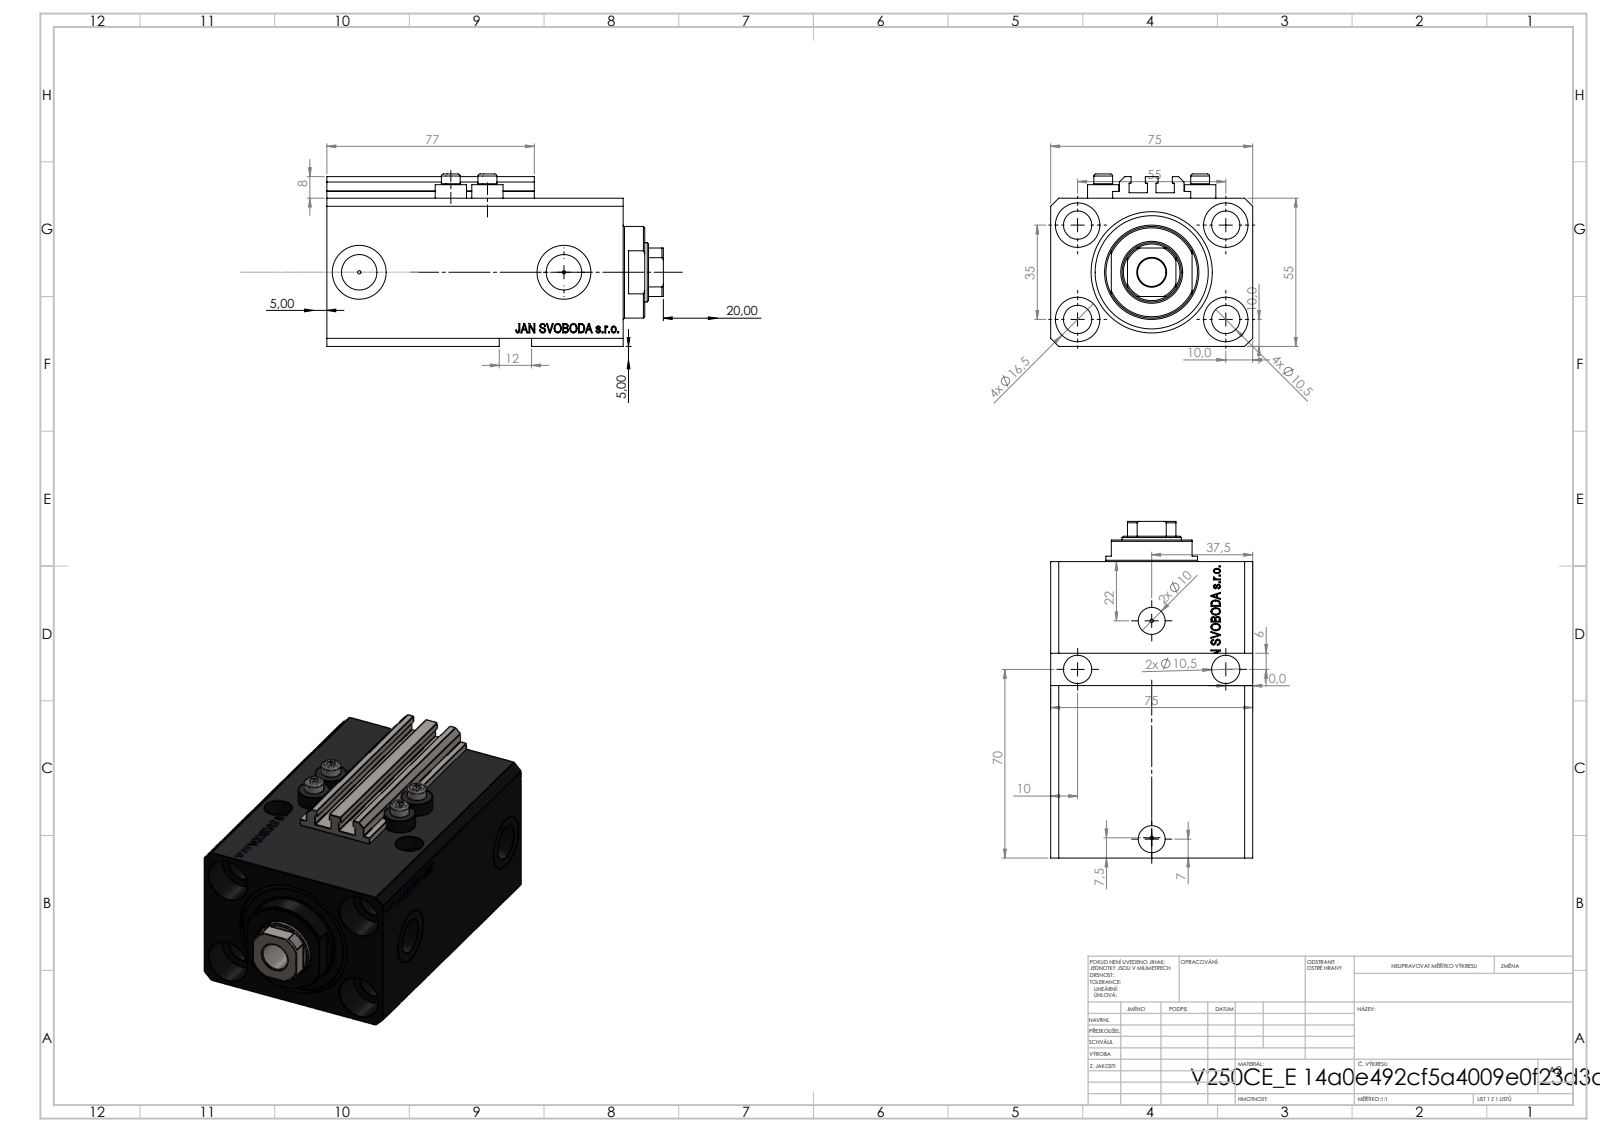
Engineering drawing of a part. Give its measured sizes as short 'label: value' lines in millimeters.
name: V250CE_E_Body; V250CE_C_VCP; ALLEN BOLT V250CE; V250CE_VC_E
written by: SolidWorks 2019 (CONFIG_CONTROL_DESIGN)
unit: mm
bodies: 8 solids, 1100 faces (518 planar, 158 cylindrical, 424 other)
size: 125 × 75 × 64
volume: 377 718 mm³; area: 96 791 mm²
holes: 9× ⌀10.5, 4× ⌀1.25, 4× ⌀4, 4× ⌀16.5, 2× ⌀10, 2× ⌀13.16, 2× ⌀20, 1× ⌀22, 1× ⌀32, 1× ⌀45
bosses: 4× ⌀11.6, 4× ⌀7, 1× ⌀34
rounds: 10× R0.2, 1× R10.5
face distances: 55, 75, 15, 110, 95, 9.9, 3, 85.1, 100.1, 57
hole spacings: 32.6, 32.87, 55, 68.74, 13.6, 14.09, 23.05, 25.81
